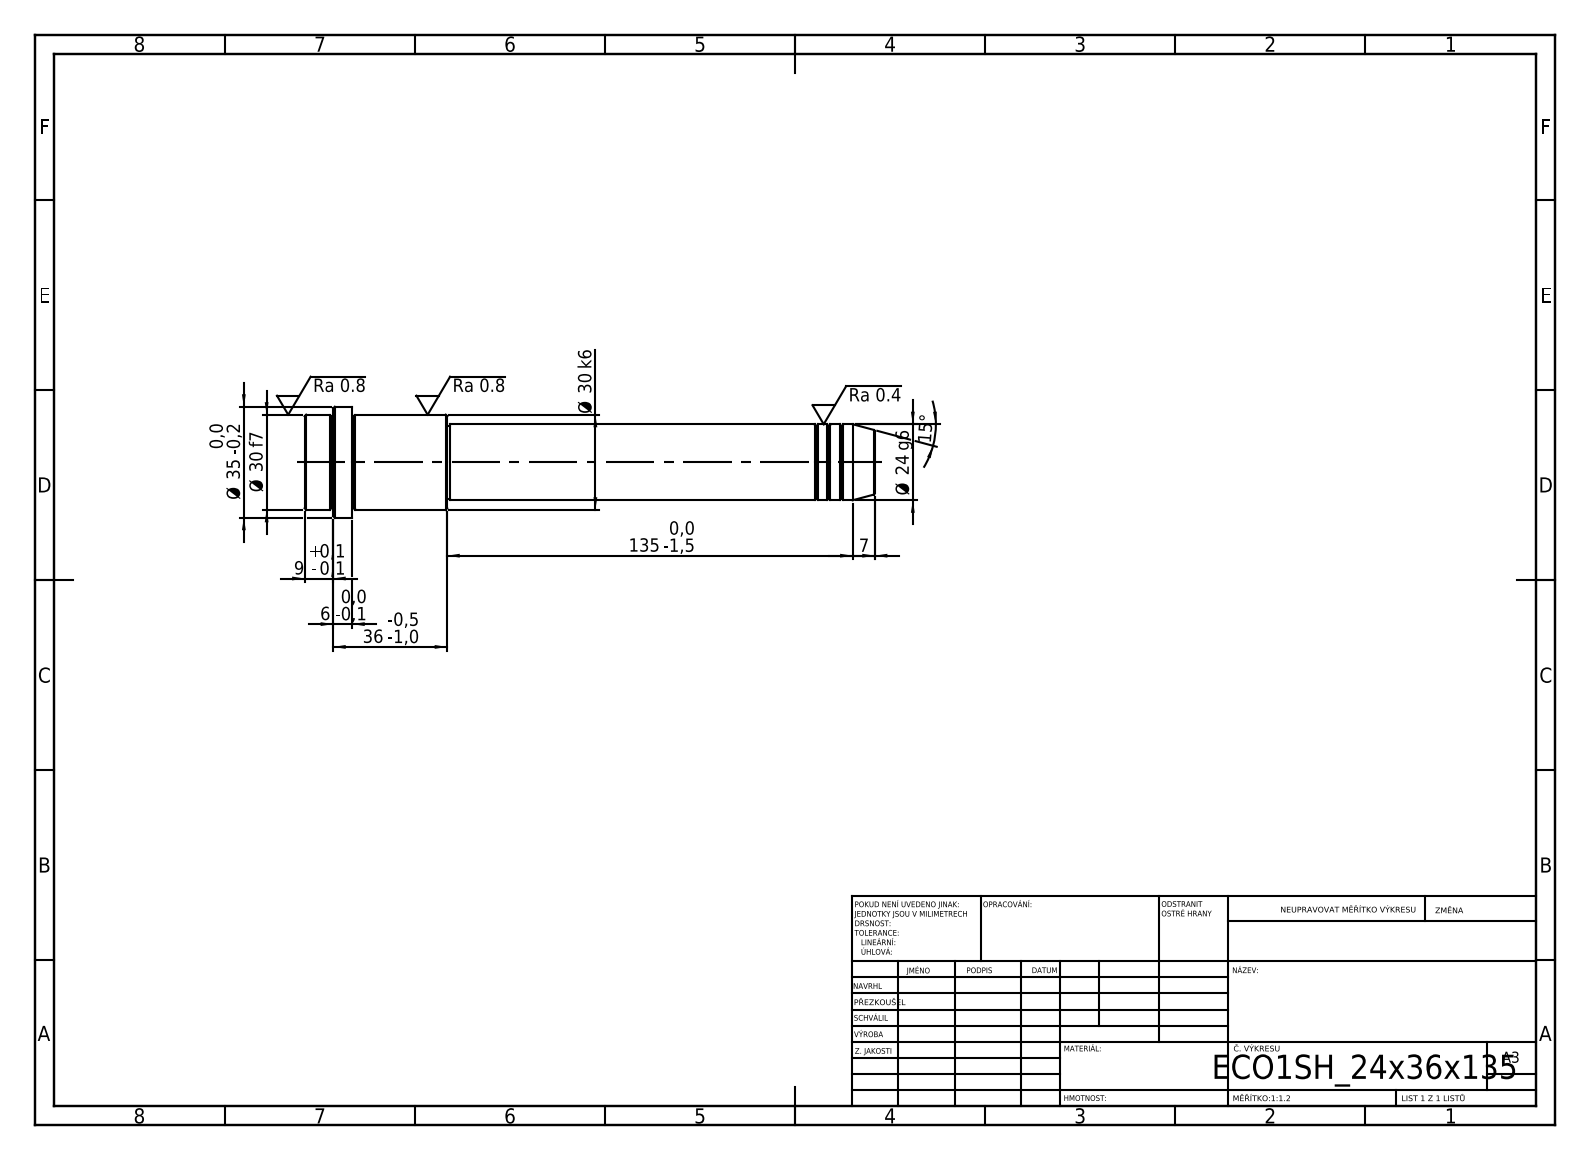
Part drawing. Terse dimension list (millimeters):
written by: SolidWorks 2019 (CONFIG_CONTROL_DESIGN)
unit: mm
bodies: 1 solid, 52 faces (6 planar, 16 cylindrical, 30 other)
size: 180 × 35 × 35
volume: 93 708 mm³; area: 16 480 mm²
bosses: 1× ⌀35, 1× ⌀30, 1× ⌀24, 1× ⌀23
face distances: 180, 165, 15, 135, 30, 45, 171, 36, 6, 9
